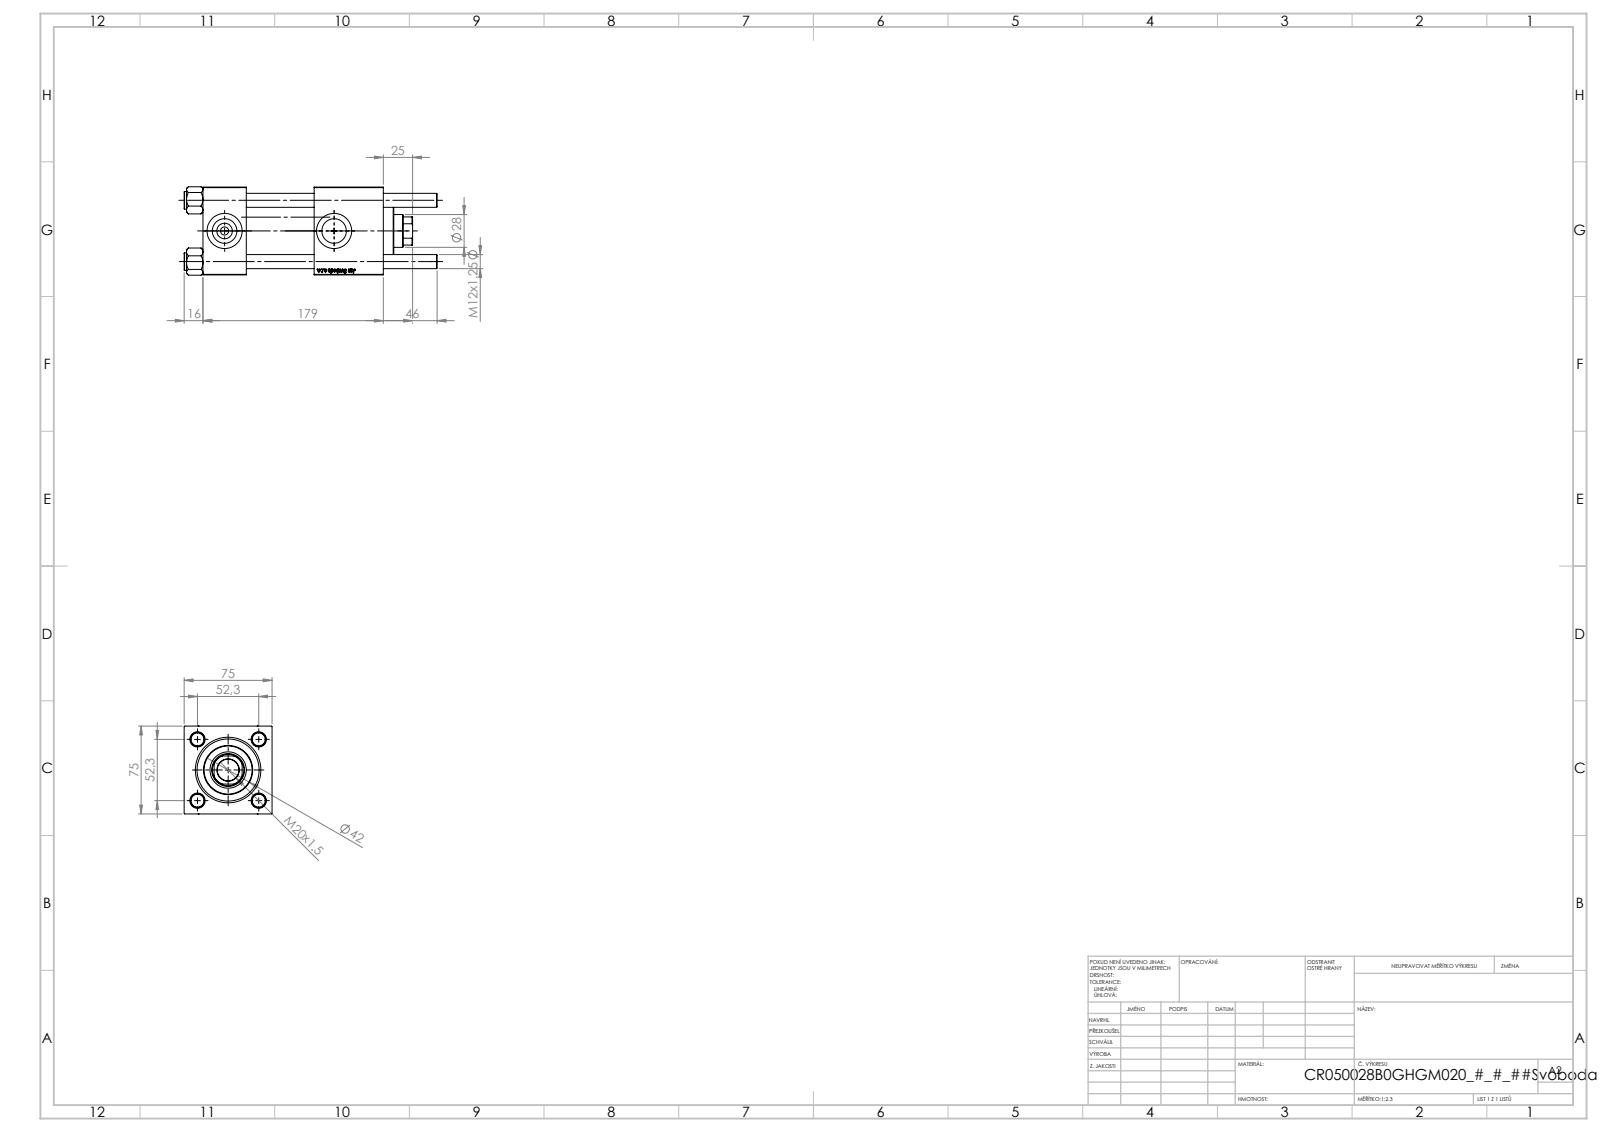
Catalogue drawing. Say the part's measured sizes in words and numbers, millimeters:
The part is named "V215CR_VCP_B; V215CR_B_TYCINKA; V215_VC_A; NUT_M5_B (+1 more)". Its 3-D file was written by "SolidWorks 2019 (CONFIG_CONTROL_DESIGN)". It is 11 solids with 1158 faces: 432 planar, 78 cylindrical and 648 other. Overall it measures 216 by 75.45 by 75 millimeters. Its volume is 702 271 cubic millimeters and its surface area 167 137 square millimeters. Round holes: 4 of diameter 12, 2 of diameter 7, 2 of diameter 20.96, 2 of diameter 30, 1 of diameter 18.5, 1 of diameter 28, 1 of diameter 31, 1 of diameter 41, 1 of diameter 50, 1 of diameter 53. Round bosses or shafts: 4 of diameter 15, 1 of diameter 56, 1 of diameter 42. Partial cylindrical surfaces (rounded edges, fillets, slot ends): 1 of radius 13.5. The main face-to-face distances are 75, 37, 154, 117, 95, 58, 59, 125.3, 88.3, 30.3. The hole center spacings are 36.98, 52.3, 73.96, 93.5.
